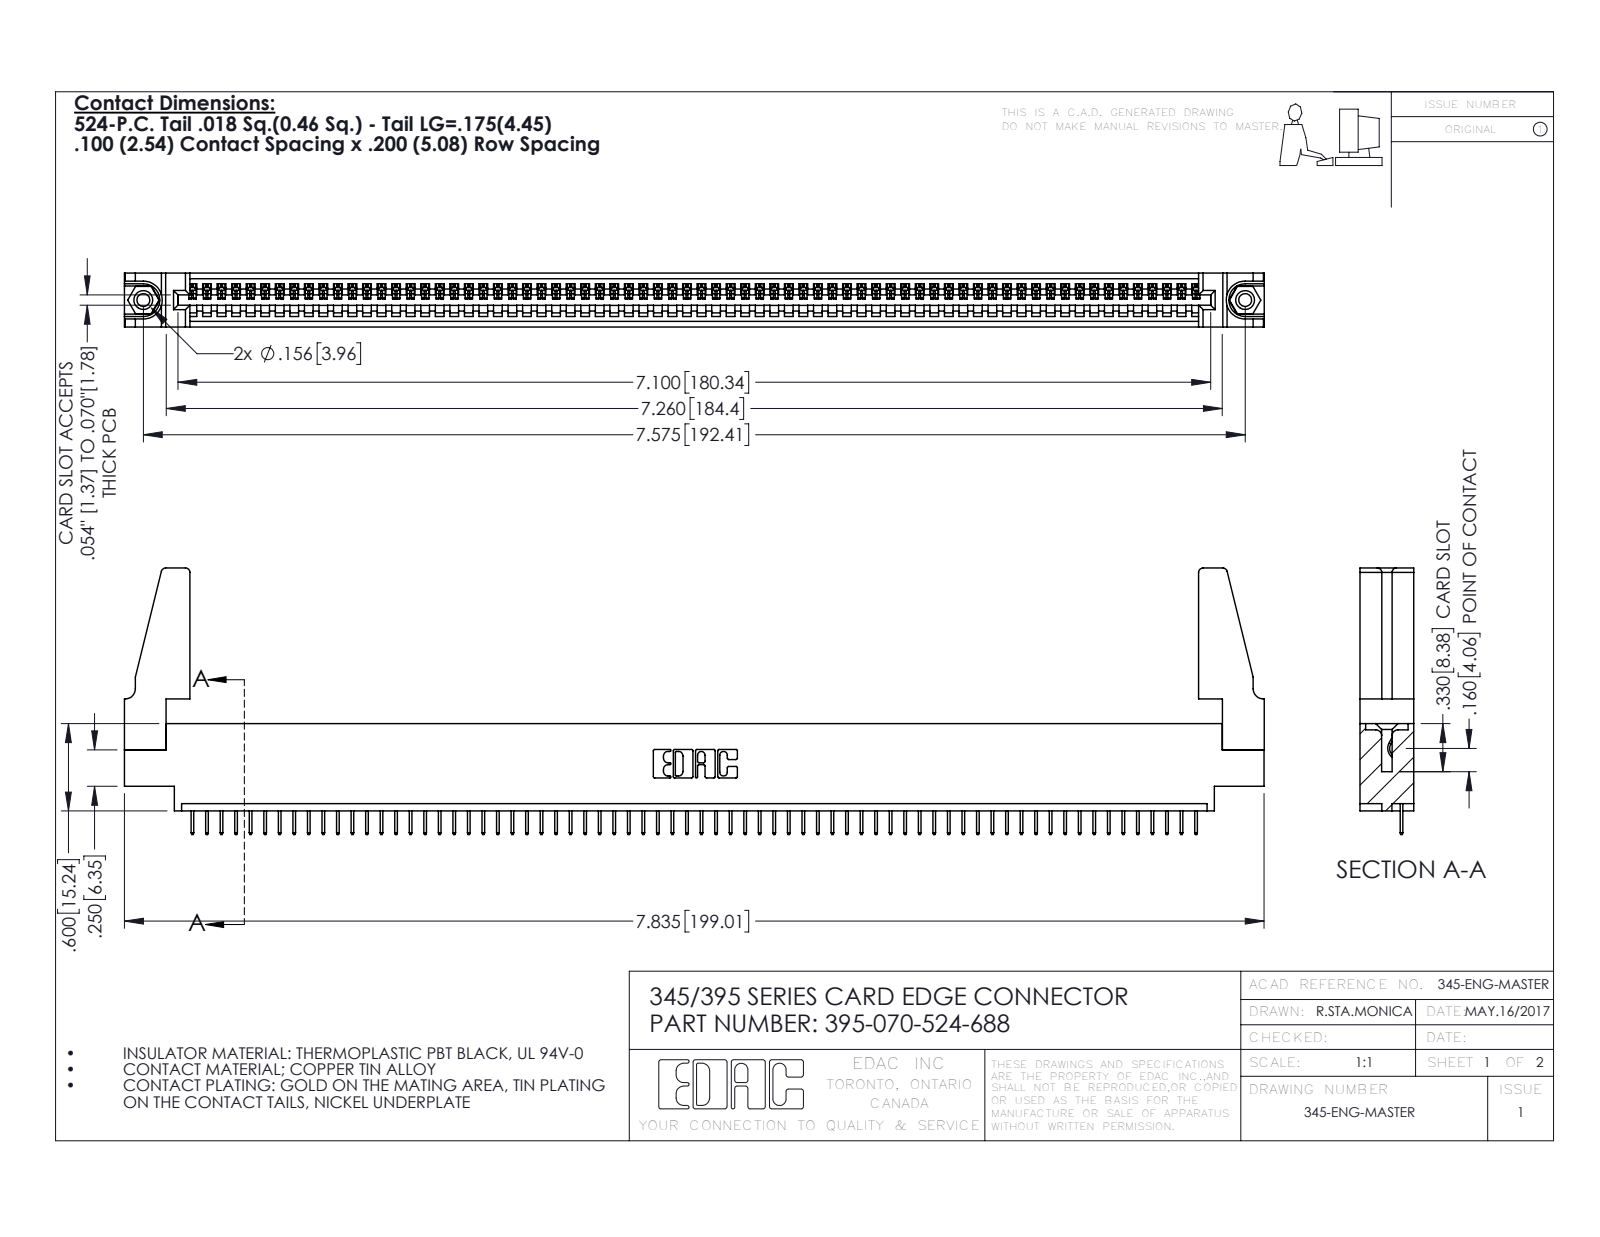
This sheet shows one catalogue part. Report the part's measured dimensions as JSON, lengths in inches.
{"part_name": "345 Part_0.170 Offset - 0.156 Dia-TH; 345-220-078_345-220-088; 395-070-524-688; 345-250-001_345-250-001-102 (+1 more)", "step_written_by": "SolidWorks 2016 (CONFIG_CONTROL_DESIGN)", "units": "inches", "bodies": {"solids": 75, "faces": 4594, "planar": 3376, "cylindrical": 1202, "other": 16}, "overall_size": [7.836, 1.832, 0.37], "volume_in3": 1.342, "surface_area_in2": 42.88, "round_holes": [[0.089, 2], [0.125, 2], [0.156, 2], [0.064, 1]], "round_bosses_or_shafts": [[0.155, 2]], "partial_cylinders_radius": [[0.006, 140], [0.01, 22], [0.03, 8], [0.007, 6], [0.031, 6], [0.026, 3], [0.031, 2], [0.04, 2]], "face_to_face_distances": [0.072, 0.298, 0.37, 0.2, 0.098, 0.272, 0.025, 0.225, 0.072, 0.175], "hole_center_spacings": [0.27, 7.339, 7.575]}
